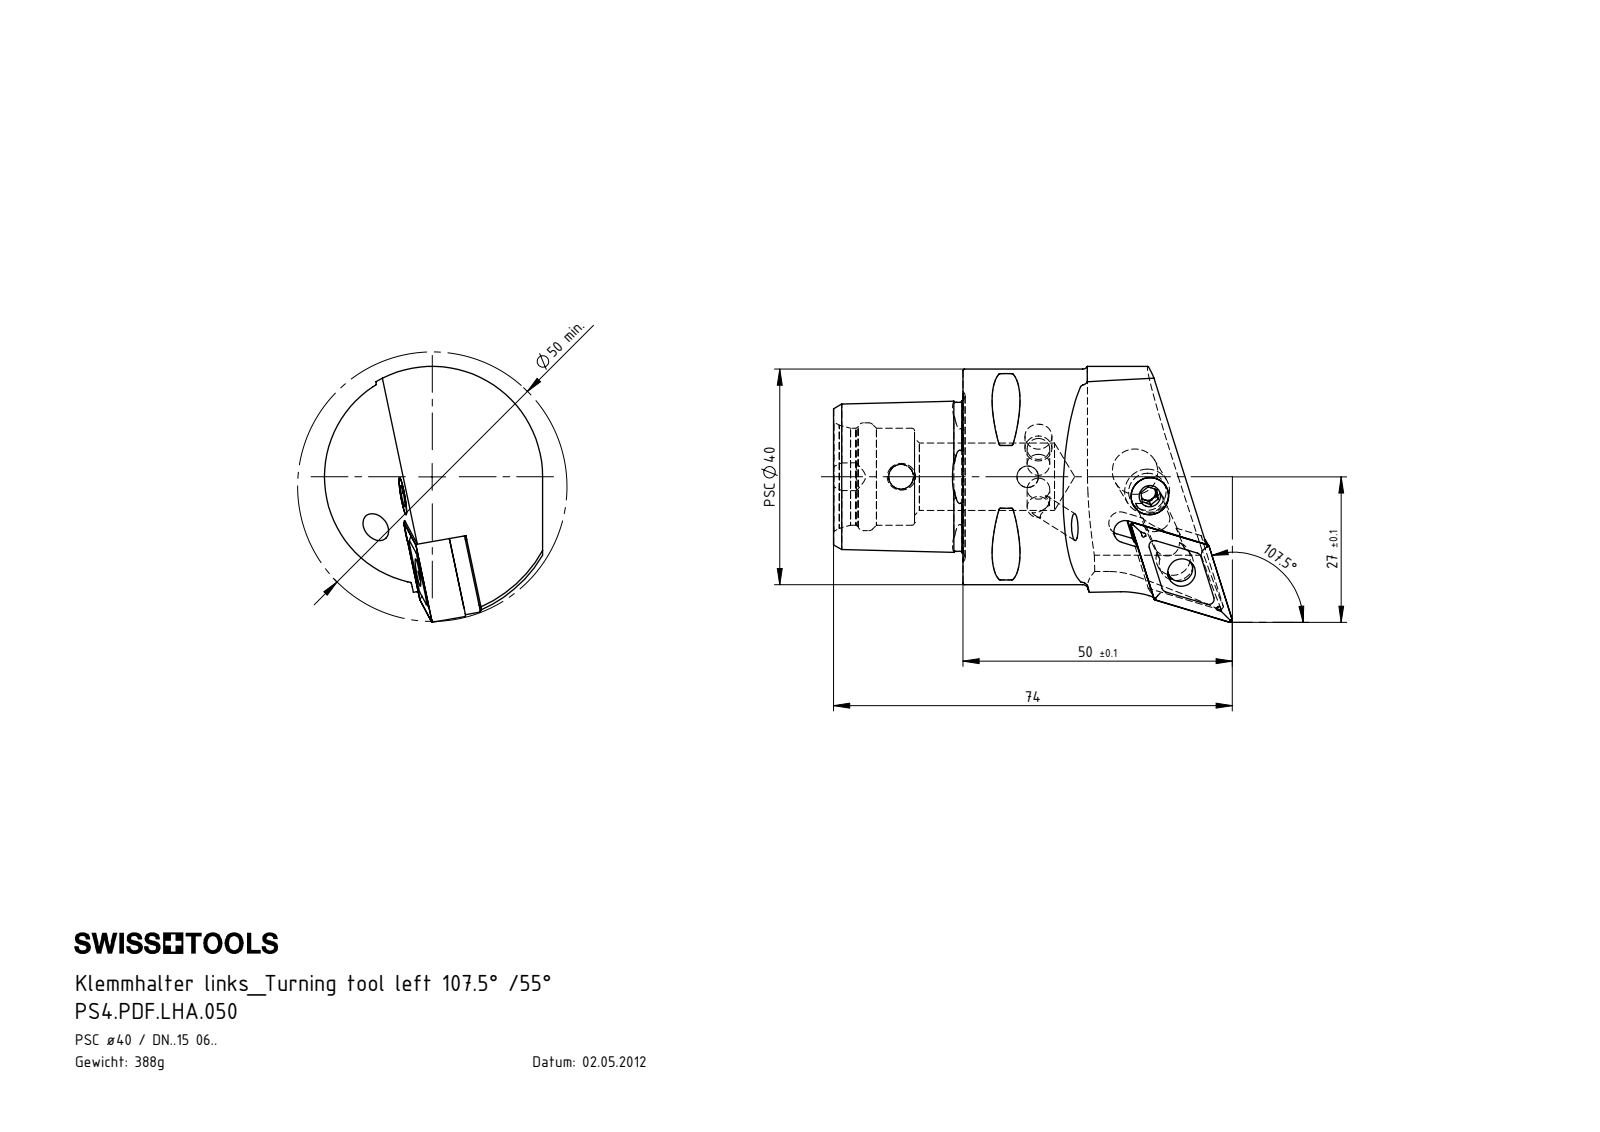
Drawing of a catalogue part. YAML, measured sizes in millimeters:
part_name: "WDF-ER2.101.003_A; WDF-ER3.101.000_A; WCD-ER4.101.017_A; WCD-ER1.101.000 (+4 more)"
step_written_by: "SolidWorks 2012 (CONFIG_CONTROL_DESIGN)"
units: millimeters
bodies: {solids: 8, faces: 345, planar: 90, cylindrical: 83, other: 172}
overall_size: [74, 47.5, 40.5]
volume: 50391
surface_area: 15878
round_holes:
  - {diameter: 4, count: 2}
  - {diameter: 4.2, count: 2}
  - {diameter: 6.4, count: 2}
  - {diameter: 4.6, count: 1}
  - {diameter: 5, count: 1}
  - {diameter: 5.16, count: 1}
  - {diameter: 7, count: 1}
  - {diameter: 8.4, count: 1}
  - {diameter: 12.5, count: 1}
  - {diameter: 18, count: 1}
  - {diameter: 20, count: 1}
round_bosses_or_shafts:
  - {diameter: 40, count: 1}
  - {diameter: 8, count: 1}
  - {diameter: 7.9, count: 1}
  - {diameter: 6.4, count: 1}
  - {diameter: 5, count: 1}
  - {diameter: 4.7, count: 1}
  - {diameter: 3.55, count: 1}
partial_cylinders:
  - {radius: 0.3, count: 8}
  - {radius: 0.4, count: 4}
  - {radius: 1, count: 4}
  - {radius: 2.5, count: 2}
  - {radius: 0.8, count: 1}
  - {radius: 2.1, count: 1}
  - {radius: 2.35, count: 1}
  - {radius: 2.8, count: 1}
face_to_face_distances: [6.05, 12.7, 12.34, 24, 3.17, 9.22, 3.18, 9.23, 0.36, 15.52]
hole_center_spacings: [15.61, 23.5]
